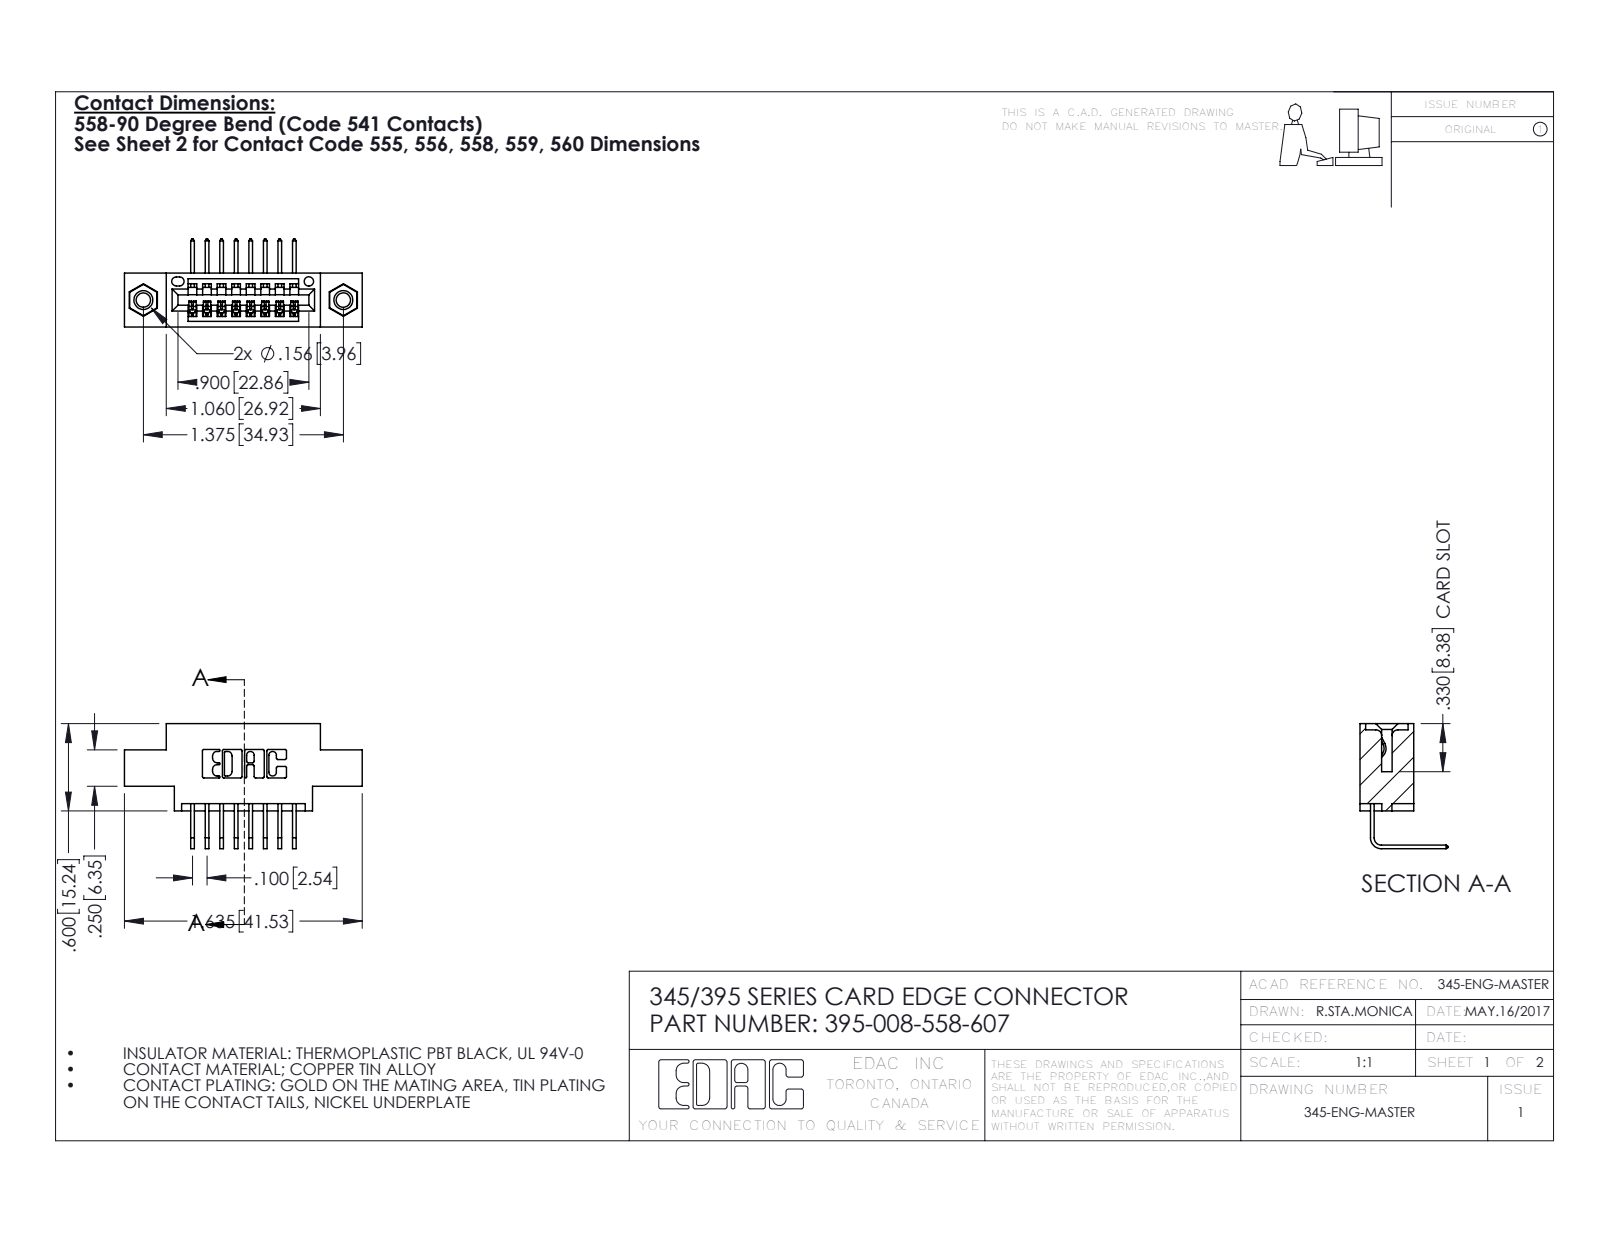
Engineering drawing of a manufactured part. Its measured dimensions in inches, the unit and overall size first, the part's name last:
Units: inches
Overall size (bounding box): 1.635 × 0.859 × 0.605
Round holes (diameter × count): ⌀0.098 ×2, ⌀0.125 ×2, ⌀0.156 ×2, ⌀0.064 ×1
Round bosses / shafts (diameter × count): ⌀0.155 ×2
Partial cylindrical surfaces — rounded edges, fillets, slot ends (radius × count): R0.01 ×22, R0.006 ×16, R0.007 ×6, R0.031 ×6, R0.026 ×3, R0.031 ×2, R0.04 ×2, R0.014 ×1
Main face-to-face distances: 0.37, 0.2, 0.072, 0.298, 0.1, 0.098, 0.272, 0.025, 0.06, 0.6
Hole centre spacings: 0.27, 1.144, 1.375
Volume: 0.218 in³ · Surface area: 7.118 in²
Bodies: 11 solids, 670 faces (452 planar, 202 cylindrical, 16 other)
Part name (STEP PRODUCT): 395-008-558-607; 345-250-001_345-250-005-103; 345 Part_0.170 Offset - 0.156 Dia-TI; 345-292-001_558 Tail - 2
STEP written by: SolidWorks 2016 (CONFIG_CONTROL_DESIGN)
